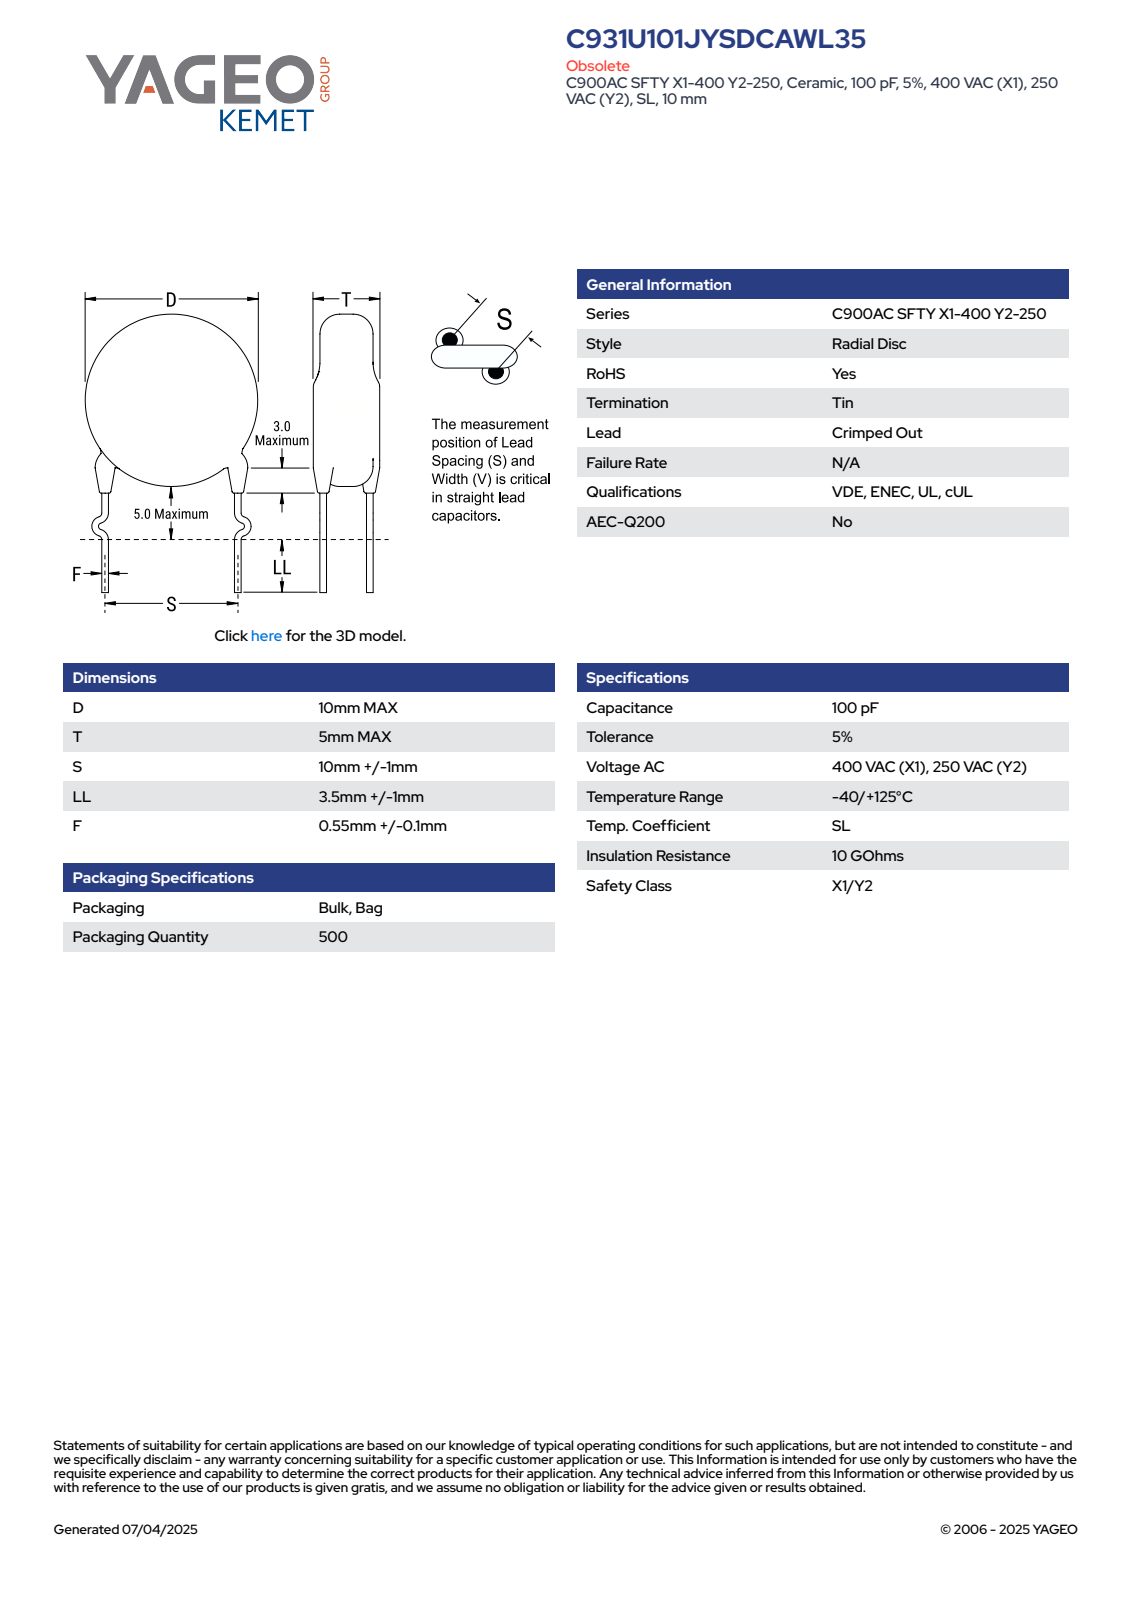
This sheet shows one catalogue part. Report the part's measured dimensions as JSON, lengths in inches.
{"part_name": "CCD_KCOC900_D10T5S10LL4.5F0.55", "step_written_by": "SolidWorks 2014 (AUTOMOTIVE_DESIGN)", "units": "inches", "bodies": {"solids": 4, "faces": 87, "planar": 63, "cylindrical": 6, "other": 18}, "overall_size": [0.768, 0.579, 0.215], "volume_in3": 0.024, "surface_area_in2": 0.566, "round_bosses_or_shafts": [[0.047, 2], [0.394, 1]], "face_to_face_distances": [0.197, 0.041, 0.218, 0.177, 0.033, 0.167, 0.015, 0.178, 0.121, 0.126]}
